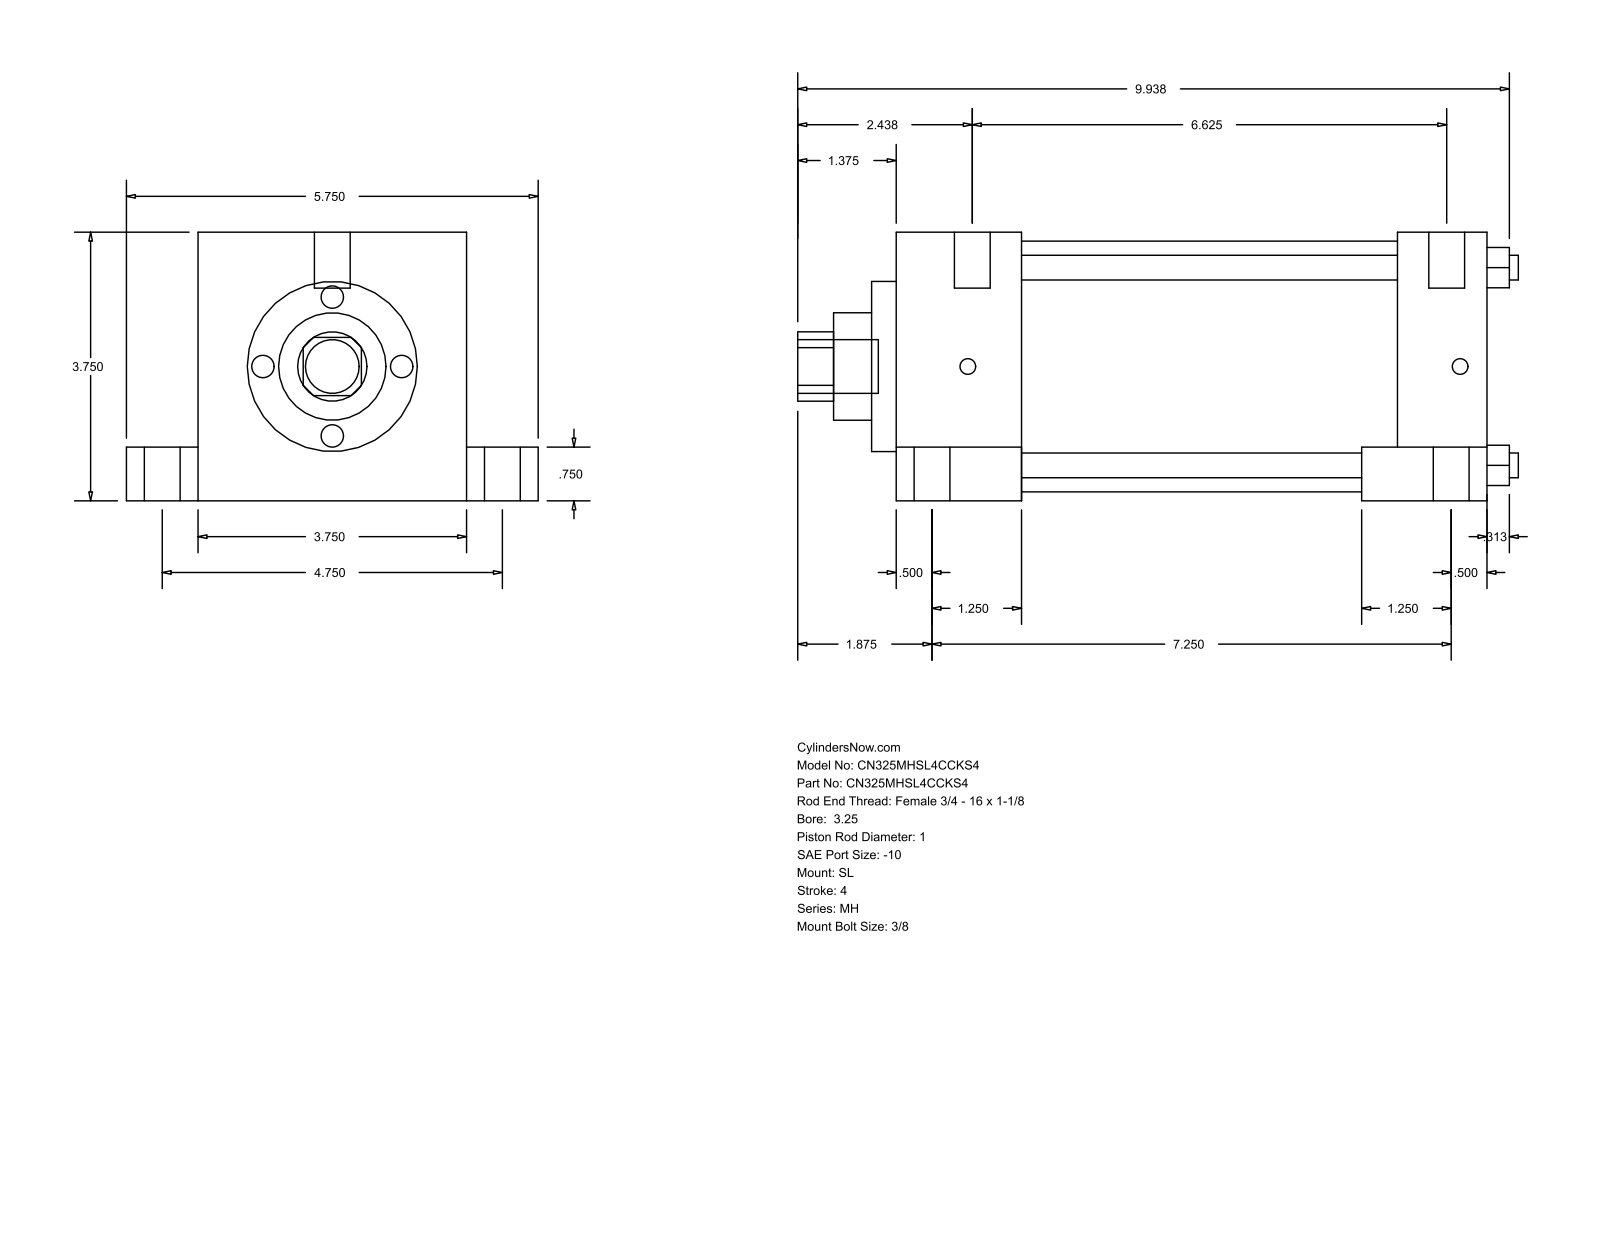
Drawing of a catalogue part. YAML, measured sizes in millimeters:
part_name: "MH_SL__0325_1"
step_written_by: "GSSL Pune (CONFIG_CONTROL_DESIGN)"
units: millimeters
bodies: {solids: 0, faces: 110, planar: 77, cylindrical: 33, other: 0}
overall_size: [255.59, 146.05, 95.25]
round_holes:
  - {diameter: 8.76, count: 4}
  - {diameter: 25.4, count: 1}
  - {diameter: 38.1, count: 1}
  - {diameter: 60.33, count: 1}
  - {diameter: 88.9, count: 1}
round_bosses_or_shafts:
  - {diameter: 12.7, count: 6}
  - {diameter: 19.05, count: 5}
  - {diameter: 5.56, count: 4}
partial_cylinders:
  - {radius: 12.29, count: 1}
face_to_face_distances: [95.24, 209.55, 120.65, 44.46, 165.09, 25.41, 19.05, 76.19, 177.8, 133.34]
hole_center_spacings: [49.57, 70.1, 99.14]
